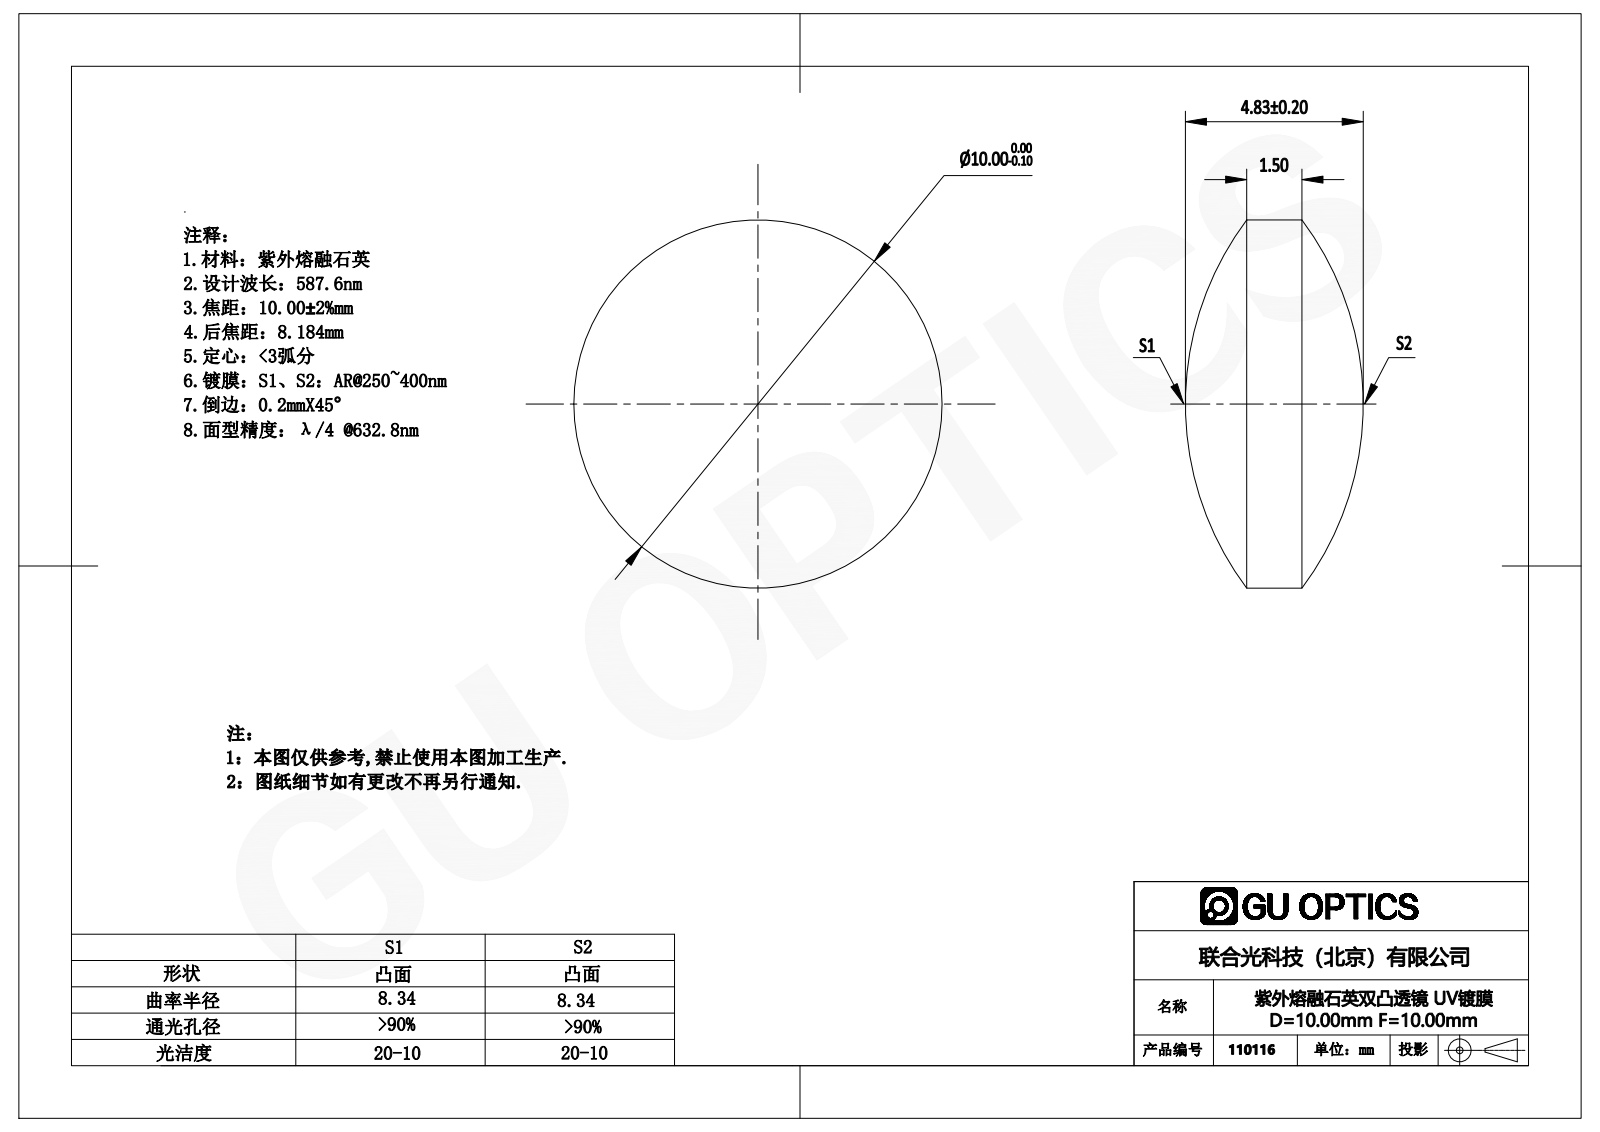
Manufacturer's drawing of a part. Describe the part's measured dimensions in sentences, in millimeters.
The part is named "110092". Its 3-D file was written by "SolidWorks 2016 (CONFIG_CONTROL_DESIGN)". It is 1 solid with 6 faces: 0 planar, 2 cylindrical and 4 other. Overall it measures 10 by 10 by 4.83 millimeters. Its volume is 253 cubic millimeters and its surface area 222 square millimeters. Round bosses or shafts: 1 of diameter 10.
